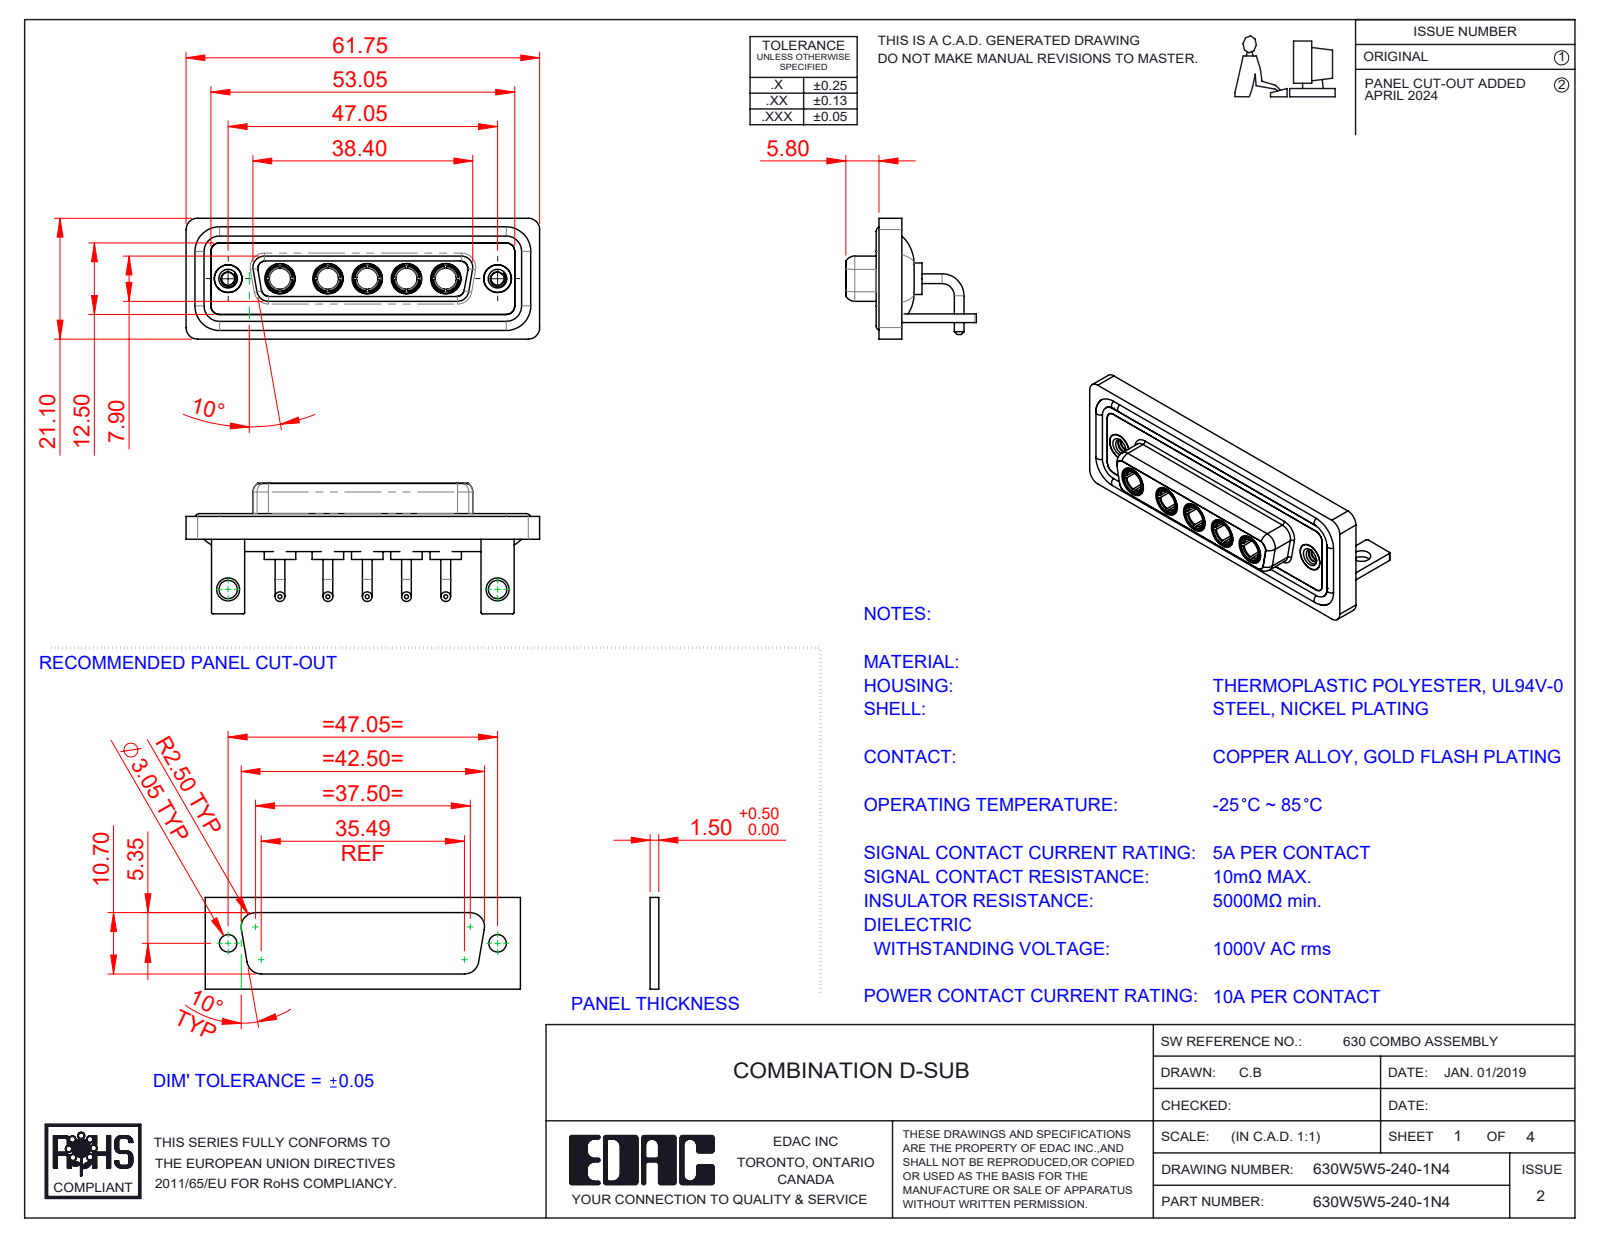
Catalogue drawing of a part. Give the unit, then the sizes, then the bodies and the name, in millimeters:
Units: millimetres
Overall size (bounding box): 61.75 × 22.8 × 21.1
Round holes (diameter × count): ⌀4.85 ×7, ⌀3.7 ×5, ⌀5.3 ×5, ⌀2.26 ×2, ⌀3.2 ×2, ⌀4 ×2, ⌀4.05 ×2, ⌀5 ×2
Round bosses / shafts (diameter × count): ⌀1.7 ×10, ⌀5.5 ×5, ⌀5.2 ×5, ⌀4.96 ×5, ⌀4.75 ×5, ⌀3.75 ×5, ⌀1.6 ×4, ⌀4.95 ×2
Partial cylindrical surfaces — rounded edges, fillets, slot ends (radius × count): R2 ×19, R1.5 ×18, R0.25 ×16, R1.35 ×8, R1.6 ×8, R0.5 ×5, R2.1 ×5, R0.6 ×4
Main face-to-face distances: 0.4, 1.8, 1.5, 2.9, 3.7, 4.1, 1.1, 1.4, 1.6, 2.5
Hole centre spacings: 6.86, 9.04, 38.01, 47.05, 6.87, 8.38, 13.72, 13.73
Volume: 8 513 mm³ · Surface area: 14 295 mm²
Bodies: 19 solids, 824 faces (270 planar, 337 cylindrical, 217 other)
Part name (STEP PRODUCT): 630Combo Housing_5W5; 630Combo Waterproof Housing_25 Contacts; 630Combo Stabilizer Bracket_50 Contacts; Power Socket_10A RA (+4 more)
STEP written by: SolidWorks 2023 (CONFIG_CONTROL_DESIGN)
